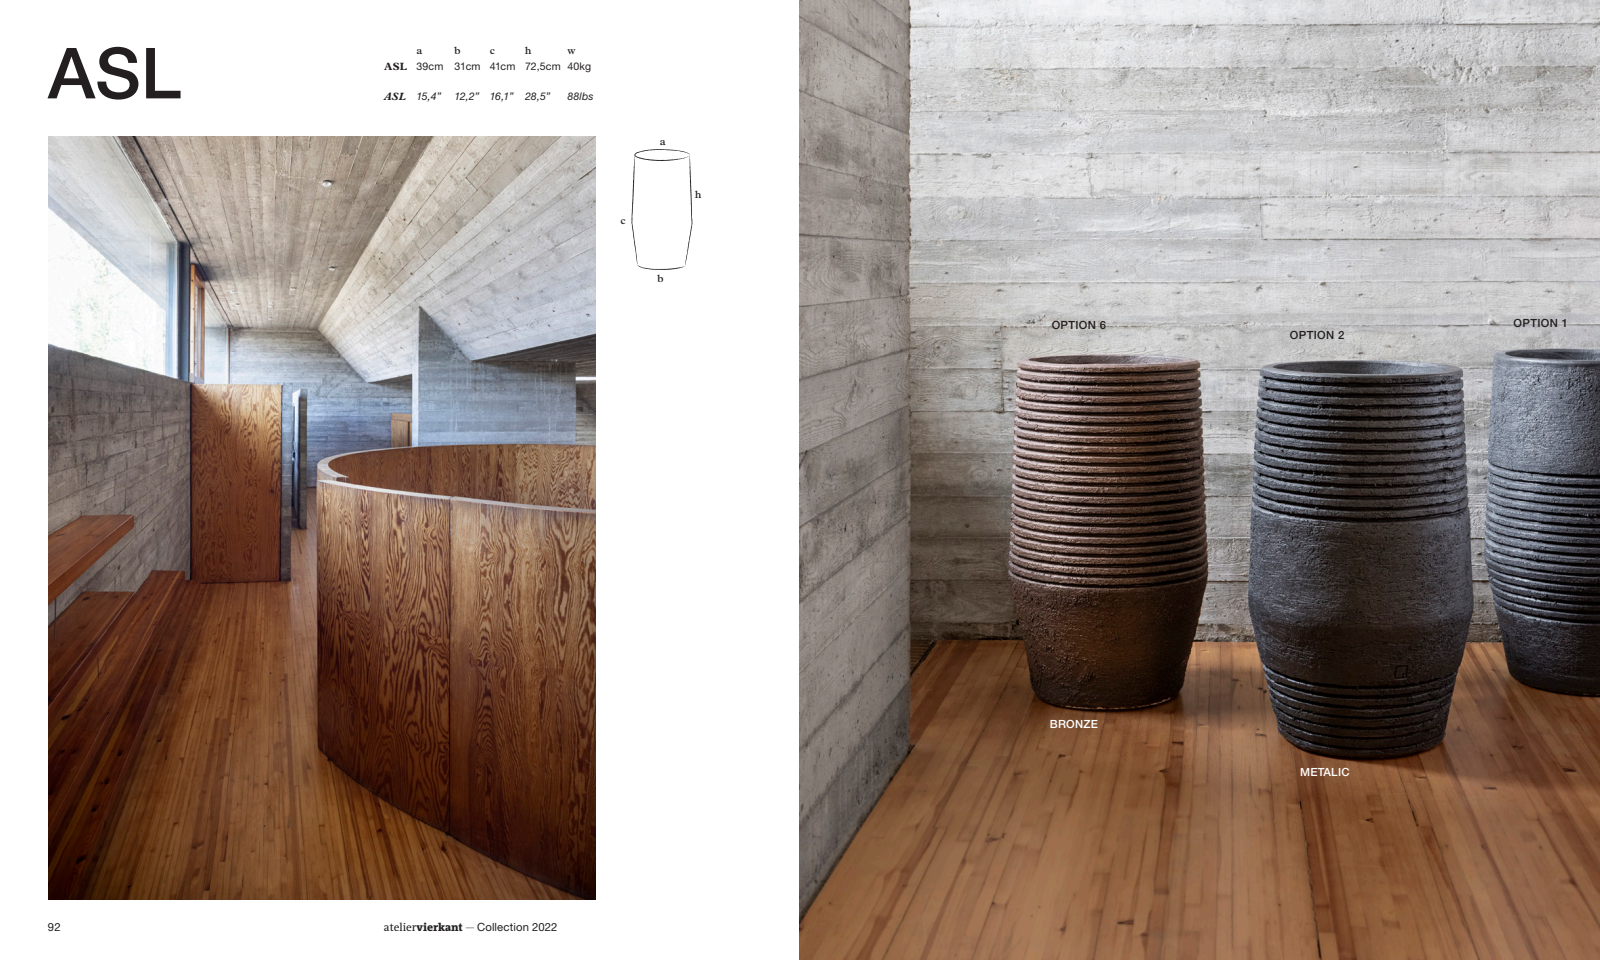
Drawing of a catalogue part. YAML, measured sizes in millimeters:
part_name: "ANILLO OCTOGONAL TAPA GRANDE; MA-ROCK T ME; CONJUNTO FLORON MARROKAIN T ME-GR; 021601400102 - TORNILLO DIN7981 DIAM.3,5X25MM ZINCADO N6 (+8 more)"
step_written_by: "SolidWorks 2013 (AUTOMOTIVE_DESIGN)"
units: millimeters
bodies: {solids: 65, faces: 21287, planar: 4756, cylindrical: 16142, other: 389}
overall_size: [1700.32, 763.76, 763.76]
volume: 1555000
surface_area: 3144000
round_holes:
  - {diameter: 6, count: 6741}
  - {diameter: 5, count: 158}
  - {diameter: 4.5, count: 35}
  - {diameter: 4, count: 18}
  - {diameter: 8.5, count: 16}
  - {diameter: 2.5, count: 7}
  - {diameter: 9, count: 5}
  - {diameter: 3, count: 4}
  - {diameter: 3.3, count: 4}
  - {diameter: 10, count: 3}
  - {diameter: 2, count: 2}
  - {diameter: 3.62, count: 2}
round_bosses_or_shafts:
  - {diameter: 5, count: 17}
  - {diameter: 1.5, count: 9}
  - {diameter: 5.5, count: 6}
  - {diameter: 4, count: 6}
  - {diameter: 12, count: 4}
  - {diameter: 7, count: 4}
  - {diameter: 6.8, count: 3}
  - {diameter: 6.5, count: 3}
partial_cylinders:
  - {radius: 3, count: 1191}
  - {radius: 0.8, count: 136}
  - {radius: 1.6, count: 136}
  - {radius: 4.5, count: 128}
  - {radius: 2.5, count: 24}
  - {radius: 1, count: 20}
  - {radius: 4, count: 18}
  - {radius: 7, count: 7}
face_to_face_distances: [0.8, 406.78, 0.79, 405.98, 406.73, 405.94, 407.53, 406.74, 407.58, 281.88]
hole_center_spacings: [12, 24, 31.75, 48, 43.27, 36, 72, 20.79]
